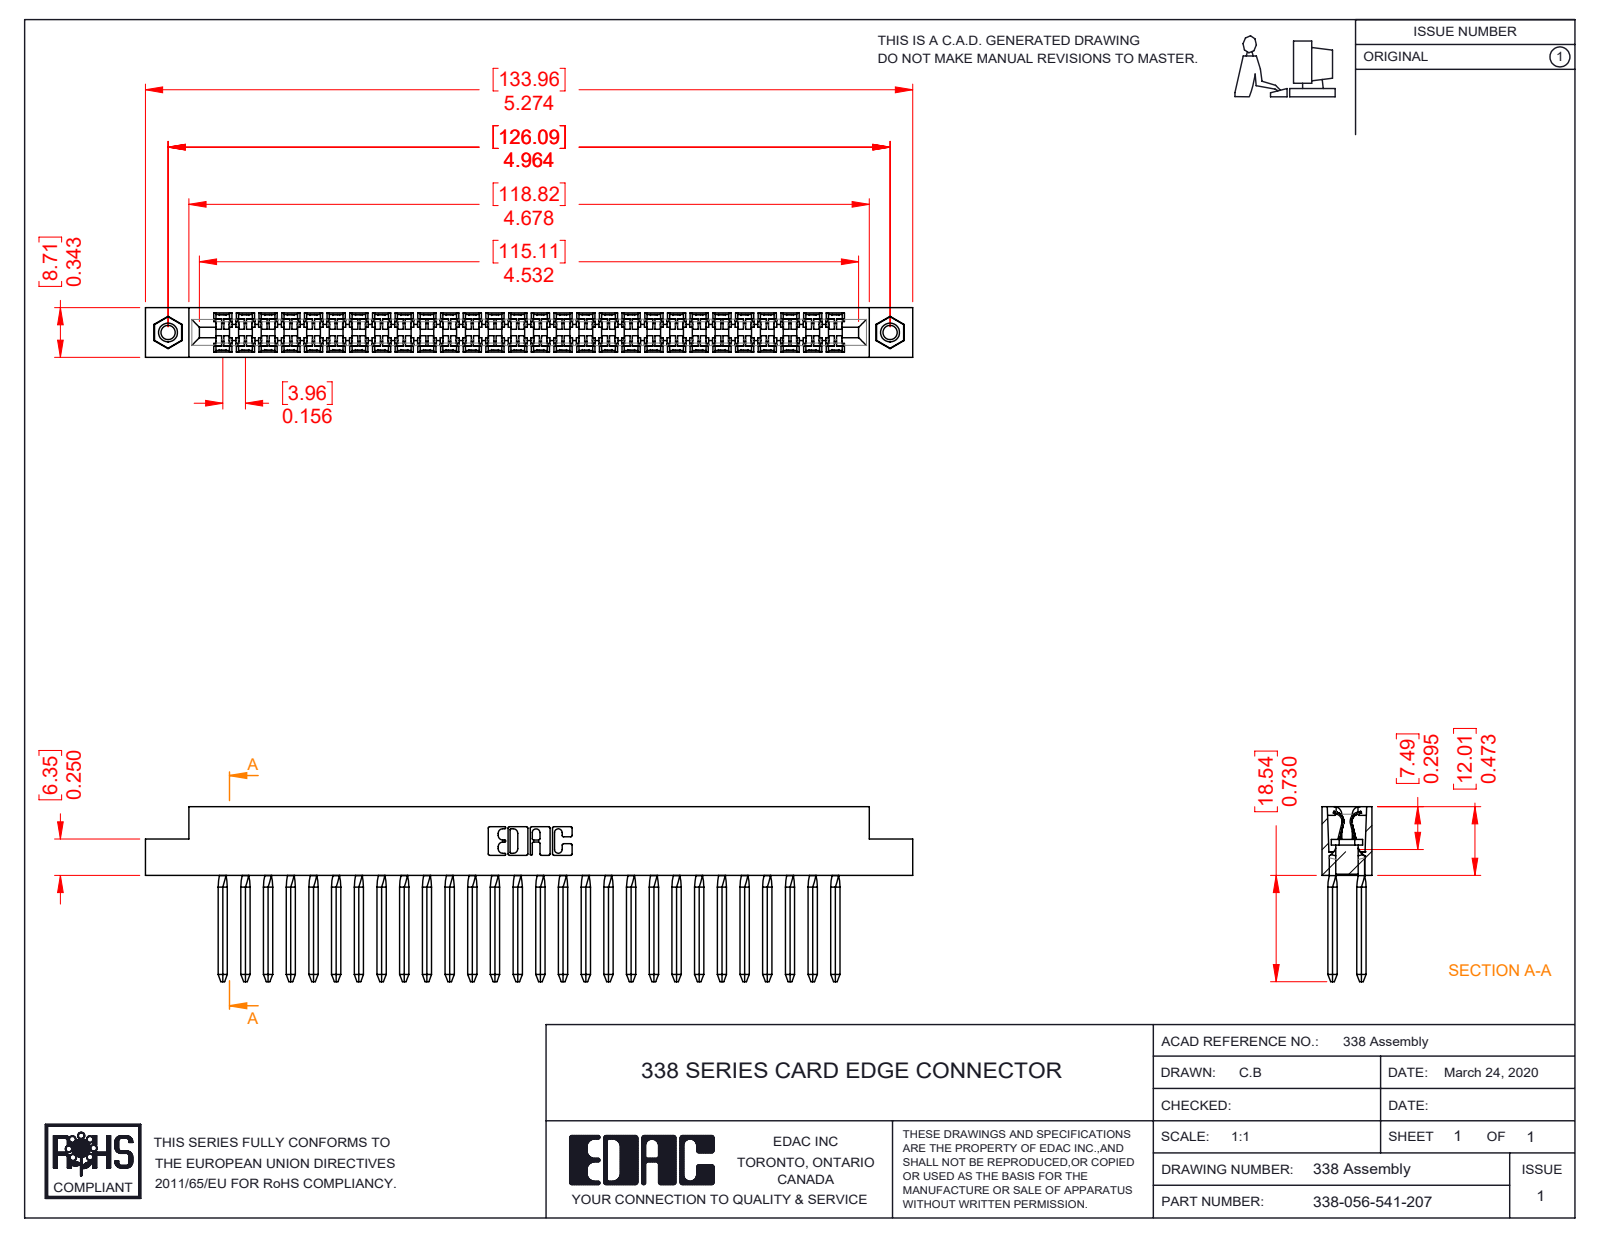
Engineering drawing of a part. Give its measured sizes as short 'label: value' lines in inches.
name: 345-250-001_345-250-005-103; 338-290-001_541; 338-210-001_338-210-028-004; 338-056-541-207
written by: SolidWorks 2016 (CONFIG_CONTROL_DESIGN)
unit: in
bodies: 59 solids, 3906 faces (2714 planar, 952 cylindrical, 240 other)
size: 5.274 × 1.203 × 0.343
volume: 0.631 in³; area: 30.27 in²
holes: 2× ⌀0.098, 2× ⌀0.125, 2× ⌀0.156
bosses: 2× ⌀0.155
rounds: 170× R0.025, 56× R0.008, 46× R0.055, 46× R0.067, 44× R0.1, 22× R0.01, 6× R0.007, 6× R0.031
face distances: 0.343, 0.156, 0.11, 0.207, 0.135, 0.624, 0.78, 0.16, 0.468, 0.048
hole spacings: 4.964
